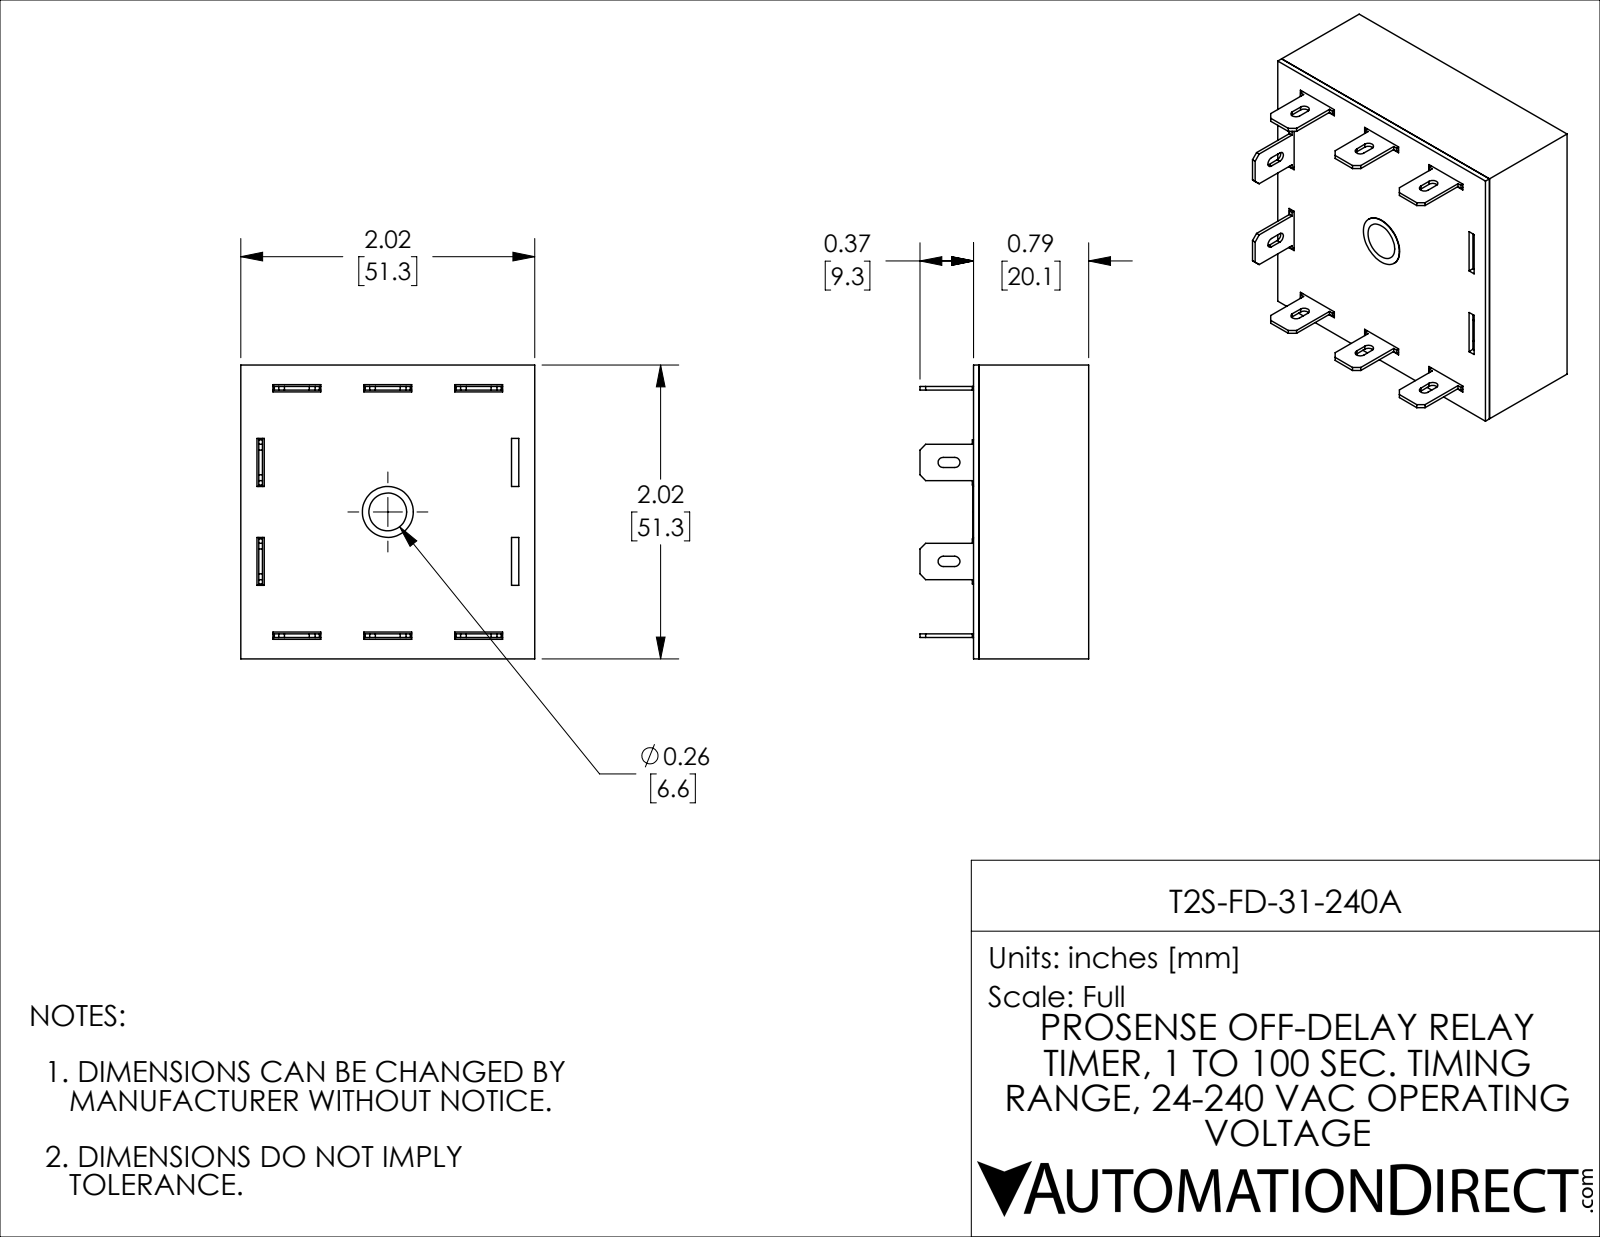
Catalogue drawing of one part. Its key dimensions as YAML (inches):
part_name: "T2S-FD-31-240A"
step_written_by: "SolidWorks 2021 (CONFIG_CONTROL_DESIGN)"
units: inches
bodies: {solids: 10, faces: 256, planar: 234, cylindrical: 20, other: 2}
overall_size: [2.02, 2.02, 1.16]
volume: 0.674
surface_area: 35.37
round_holes:
  - {diameter: 0.35, count: 1}
partial_cylinders:
  - {radius: 0.035, count: 10}
face_to_face_distances: [0.045, 1.975, 0.754, 0.792, 0.038, 0.709, 0.747, 2.02, 1.93, 0.147]
